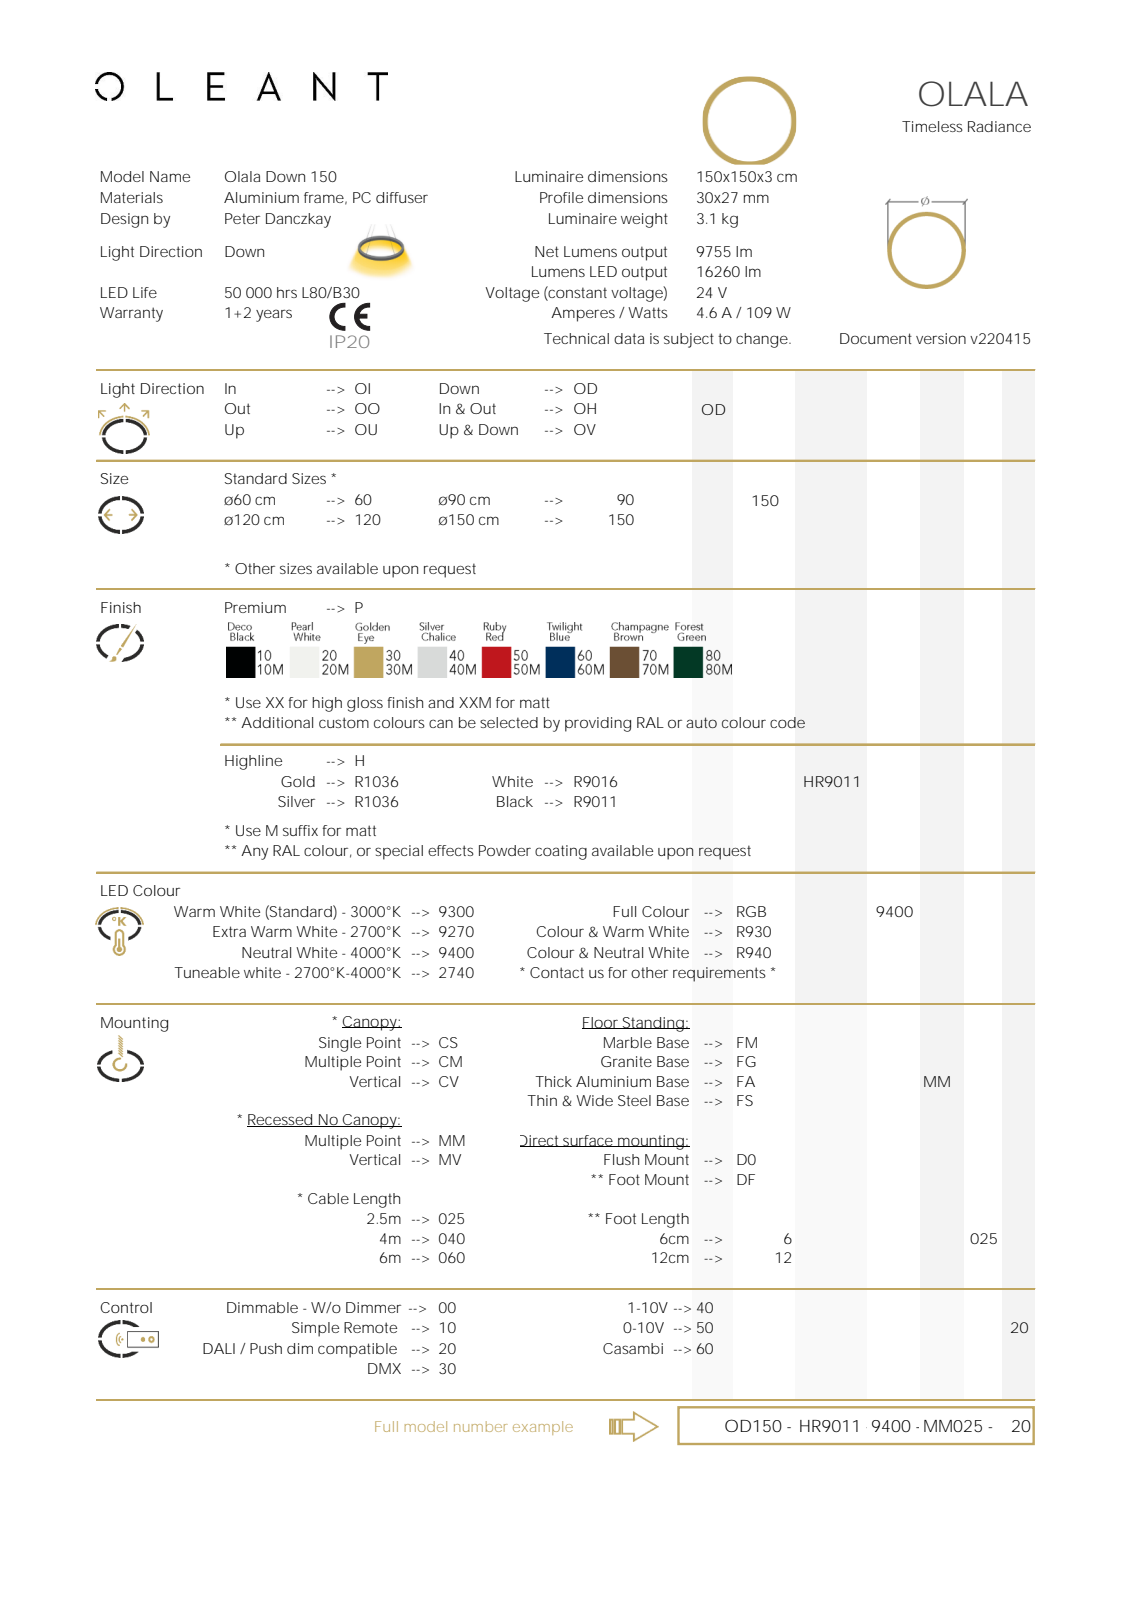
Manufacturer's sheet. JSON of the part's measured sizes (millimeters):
{"part_name": "olala; frame; plexi; cable (+1 more)", "step_written_by": "Autodesk Inventor 2020 (AUTOMOTIVE_DESIGN)", "units": "millimeters", "bodies": {"solids": 8, "faces": 114, "planar": 61, "cylindrical": 43, "other": 10}, "overall_size": [1500, 1500, 1049.5], "volume_mm3": 3634000, "surface_area_mm2": 1222000, "round_holes": [[3, 3], [1440, 1], [1496, 1]], "round_bosses_or_shafts": [[11, 3], [9, 3], [4, 3], [1.2, 3], [1500, 1], [1498, 1], [1444, 1]], "face_to_face_distances": [2, 24.5, 22.5, 26.5, 12, 12.02, 11.98, 1049.5, 1047.5, 1025], "hole_center_spacings": [735, 1273.06]}
